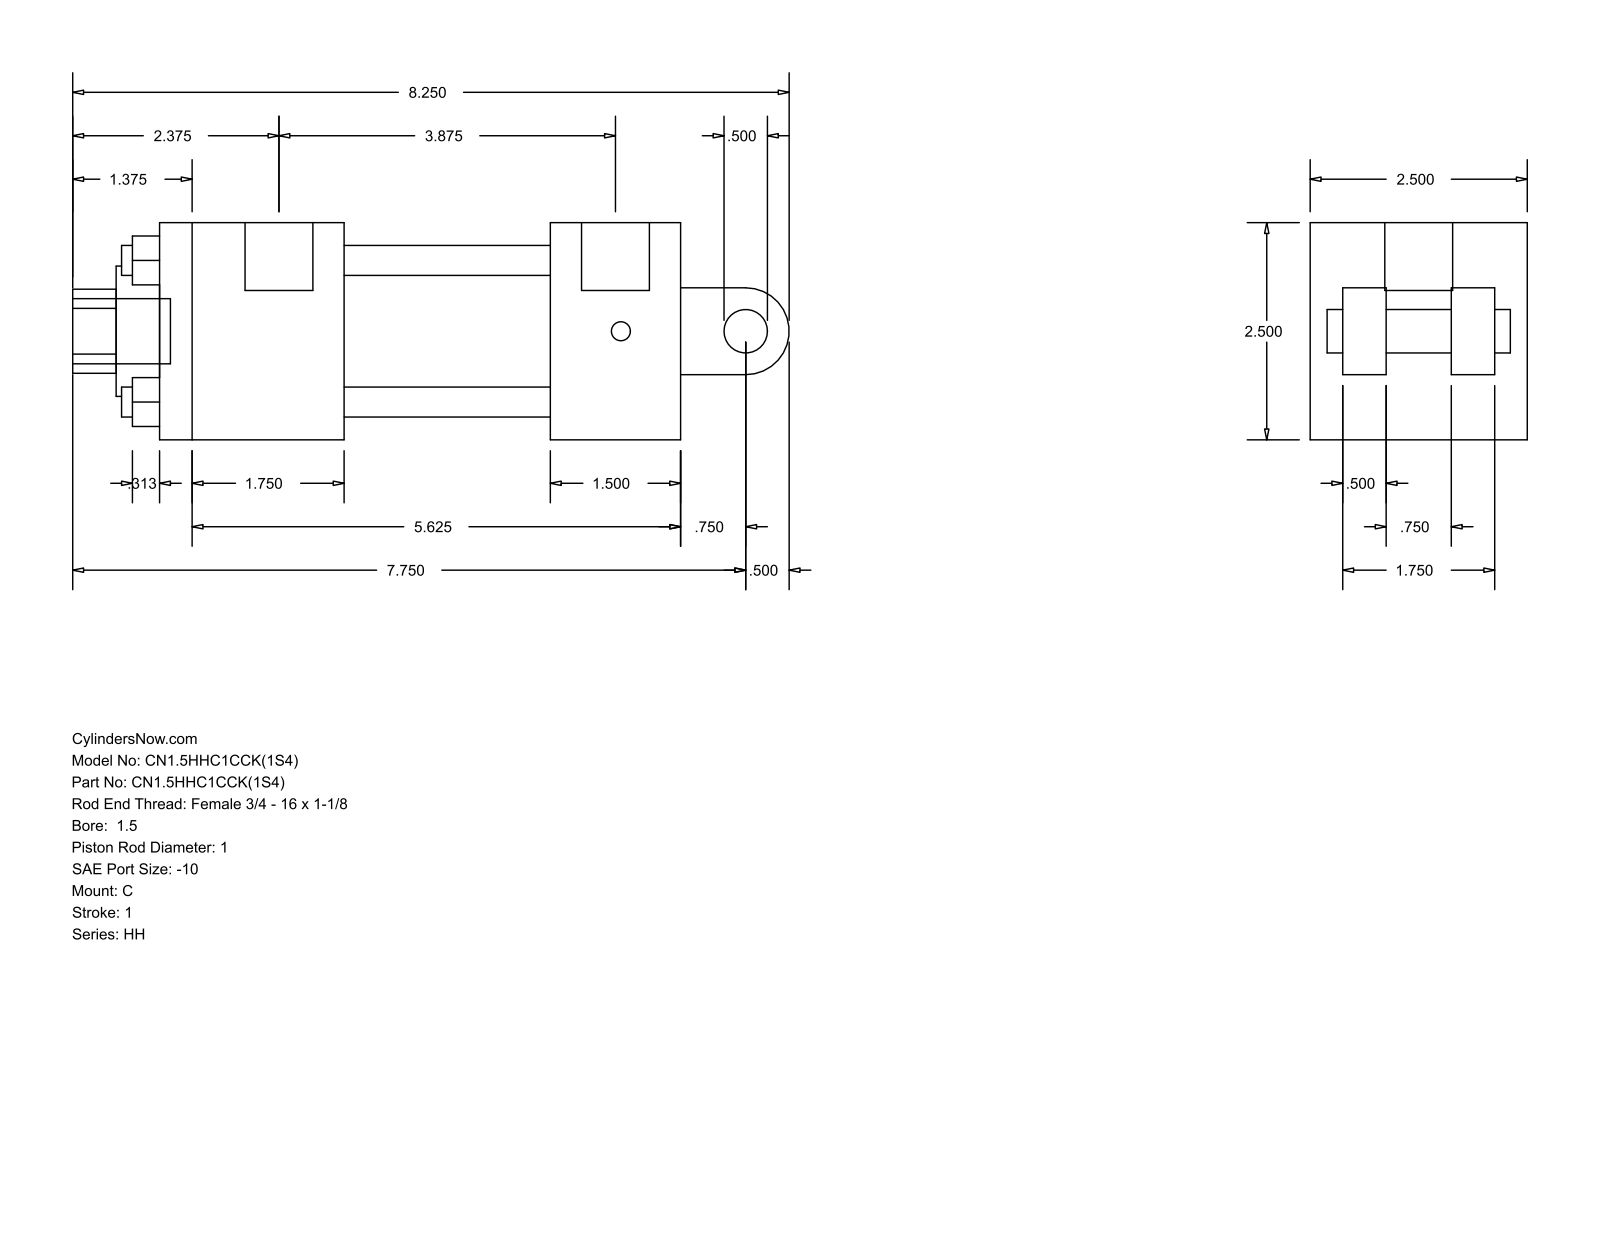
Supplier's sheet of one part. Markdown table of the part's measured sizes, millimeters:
| quantity | value |
| --- | --- |
| part name | HH_C__0150_1 |
| STEP written by | GSSL Pune (CONFIG_CONTROL_DESIGN) |
| units | millimeters |
| bodies | 0 solids, 99 faces (70 planar, 29 cylindrical, 0 other) |
| overall size | 209.55 × 63.5 × 63.5 |
| round holes (diameter × count) | 8.76 × 4, 5.56 × 2, 19.84 × 1, 25.4 × 1, 38.1 × 1, 44.45 × 1 |
| round bosses / shafts (diameter × count) | 5.56 × 2, 19.84 × 1, 19.05 × 1, 12.7 × 1 |
| partial cylindrical surfaces (radius × count) | 12.29 × 1, 12.7 × 1 |
| main face-to-face distances | 63.5, 53.98, 60.32, 98.42, 38.1, 114.3, 152.4, 12.7, 9.52, 22.22 |
| hole center spacings | 29.27, 41.4, 58.55, 1.59 |
